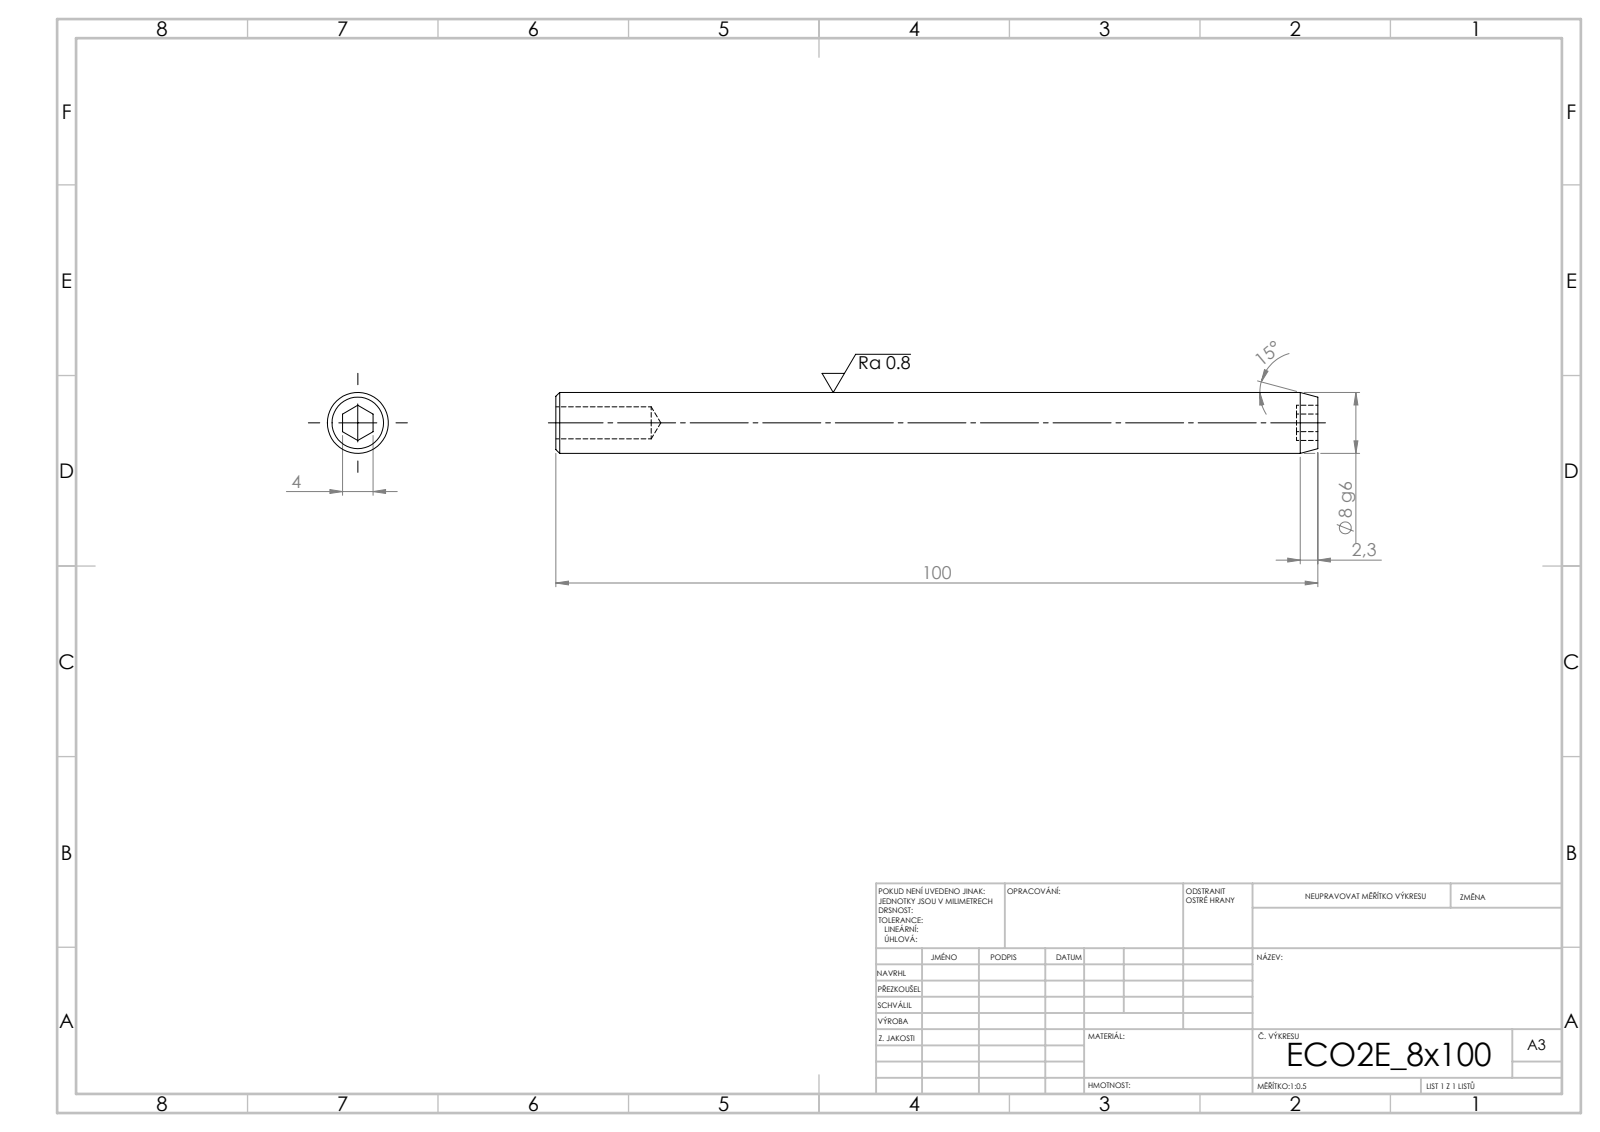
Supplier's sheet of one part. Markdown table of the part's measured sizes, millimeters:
| quantity | value |
| --- | --- |
| STEP written by | SolidWorks 2019 (CONFIG_CONTROL_DESIGN) |
| units | millimeters |
| bodies | 1 solid, 19 faces (9 planar, 4 cylindrical, 6 other) |
| overall size | 100 × 8 × 8 |
| volume | 4 789 mm³ |
| surface area | 2 795 mm² |
| round holes (diameter × count) | 4.2 × 1 |
| round bosses / shafts (diameter × count) | 8 × 1 |
| main face-to-face distances | 100, 4, 2.8, 97.2 |
